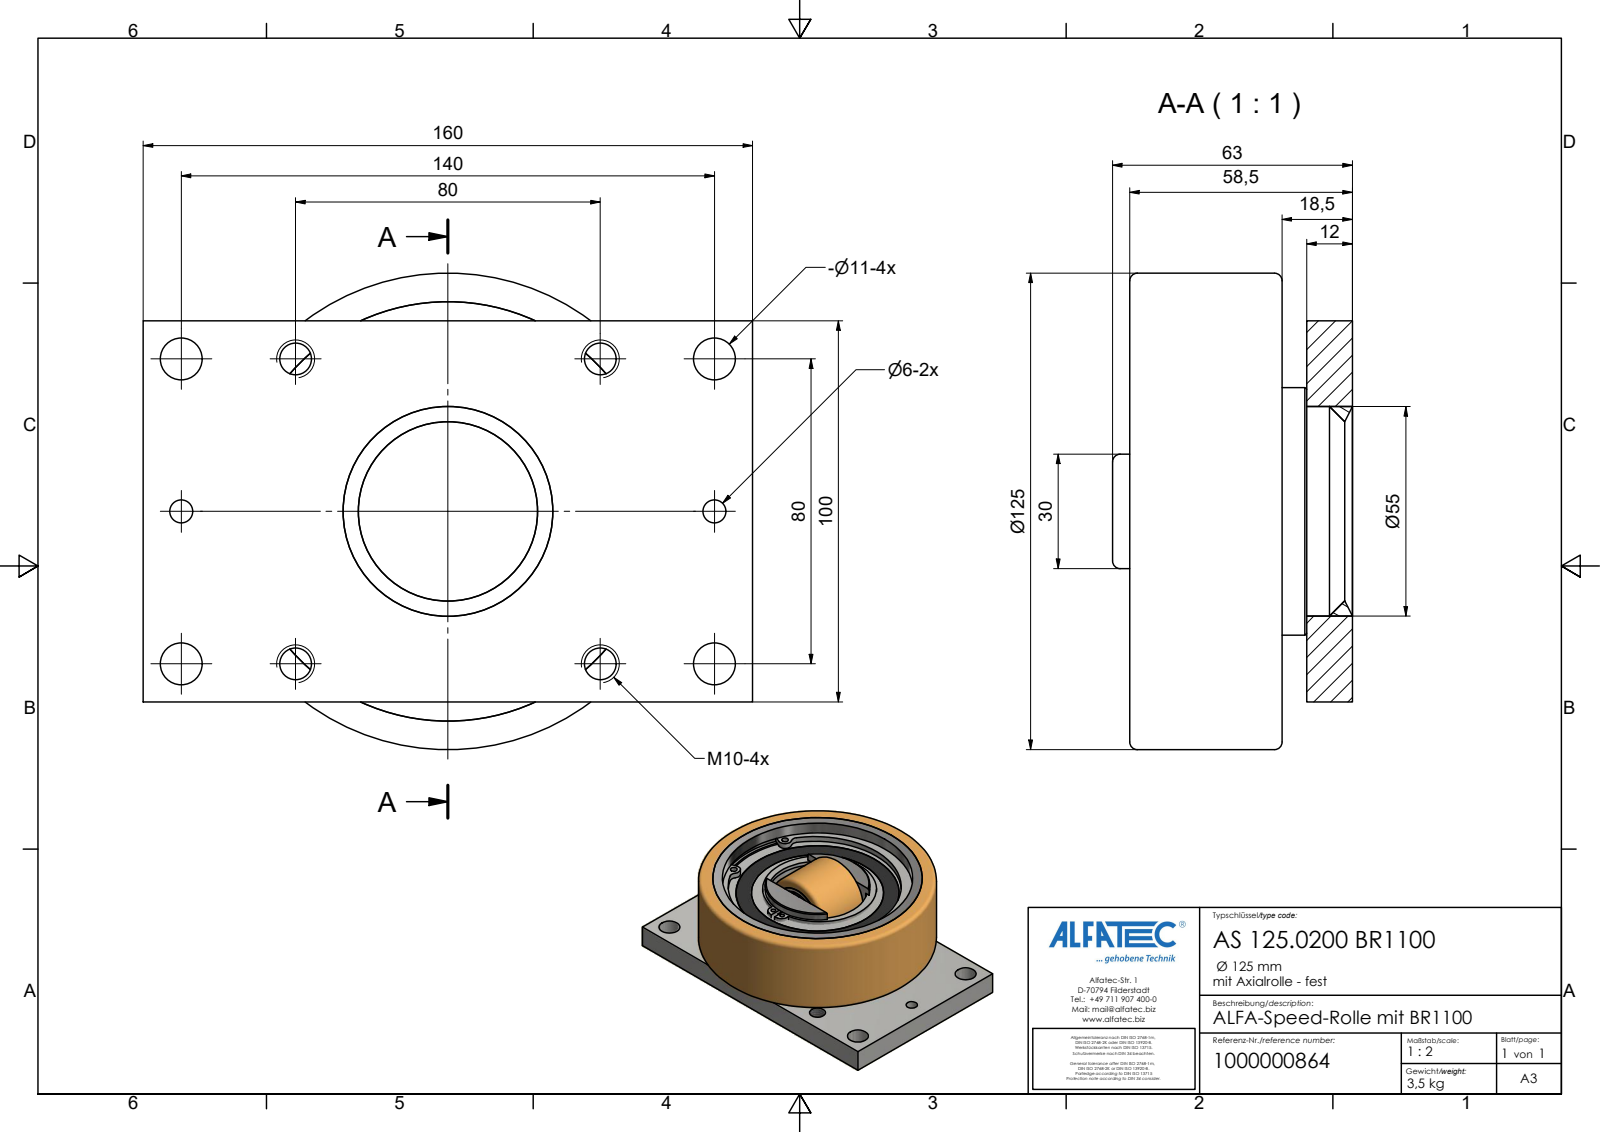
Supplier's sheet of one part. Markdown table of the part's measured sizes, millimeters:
| quantity | value |
| --- | --- |
| part name | AS 125.0200 BR1100_Kontur |
| STEP written by | Autodesk Inventor 2020 (CONFIG_CONTROL_DESIGN) |
| units | millimeters |
| bodies | 16 solids, 181 faces (51 planar, 60 cylindrical, 70 other) |
| overall size | 160 × 125 × 63 |
| volume | 546 701 mm³ |
| surface area | 118 814 mm² |
| round holes (diameter × count) | 8.38 × 4, 11 × 4, 6 × 2, 10 × 1, 20.88 × 1, 22.5 × 1, 26 × 1, 27.5 × 1, 52 × 1, 85.6 × 1, 86 × 1, 90.9 × 1 |
| round bosses / shafts (diameter × count) | 125 × 1, 69.4 × 1, 65 × 1, 59.8 × 1, 55 × 1, 40 × 1, 27.2 × 1, 15.12 × 1 |
| partial cylindrical surfaces (radius × count) | 2 × 4, 3.5 × 4, 3.75 × 2, 11.5 × 1, 25.5 × 1, 27.2 × 1 |
| main face-to-face distances | 12, 6.5, 30.5, 18.5, 40, 9.5, 49, 2, 37, 47 |
| hole center spacings | 80, 30, 40, 50, 56.57, 80.62, 85.44, 110 |
